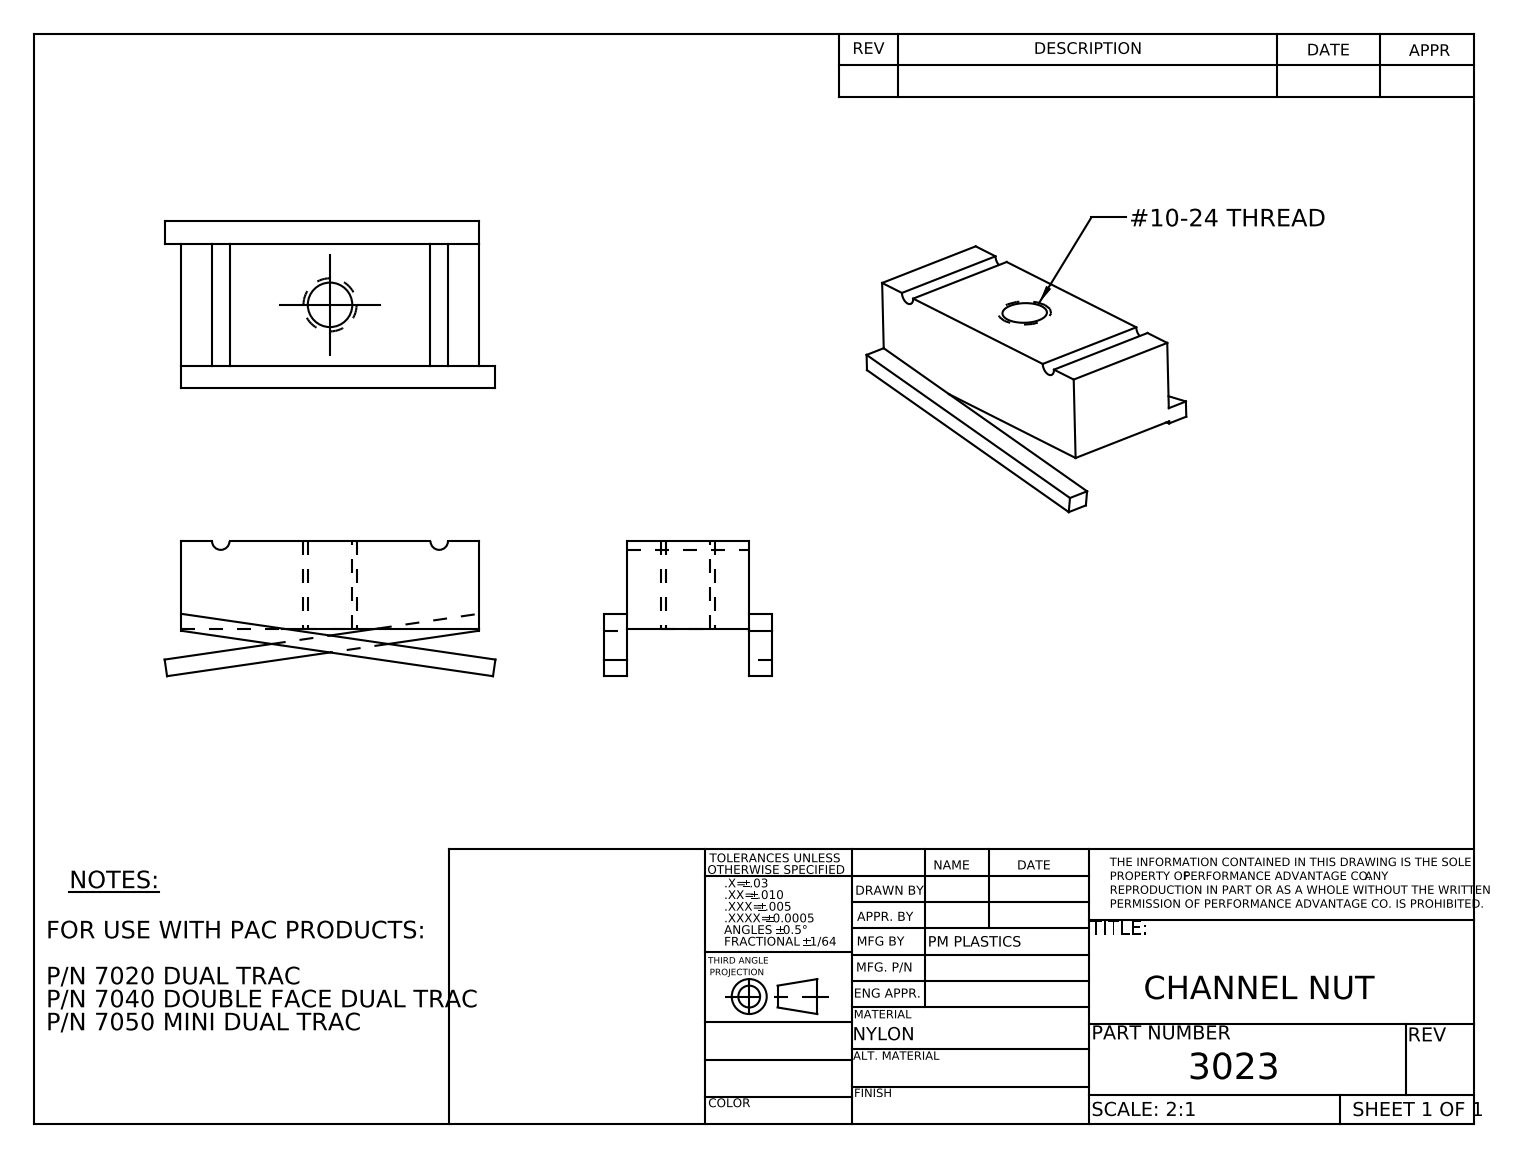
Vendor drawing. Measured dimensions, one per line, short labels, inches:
name: 3023
written by: SolidWorks 2010 (CONFIG_CONTROL_DESIGN)
unit: in
bodies: 1 solid, 24 faces (18 planar, 6 cylindrical, 0 other)
size: 1.182 × 0.597 × 0.483
volume: 0.149 in³; area: 2.623 in²
holes: 1× ⌀0.159
rounds: 2× R0.031
face distances: 0.313, 0.438, 0.06, 1.062, 0.08, 0.518, 0.598
